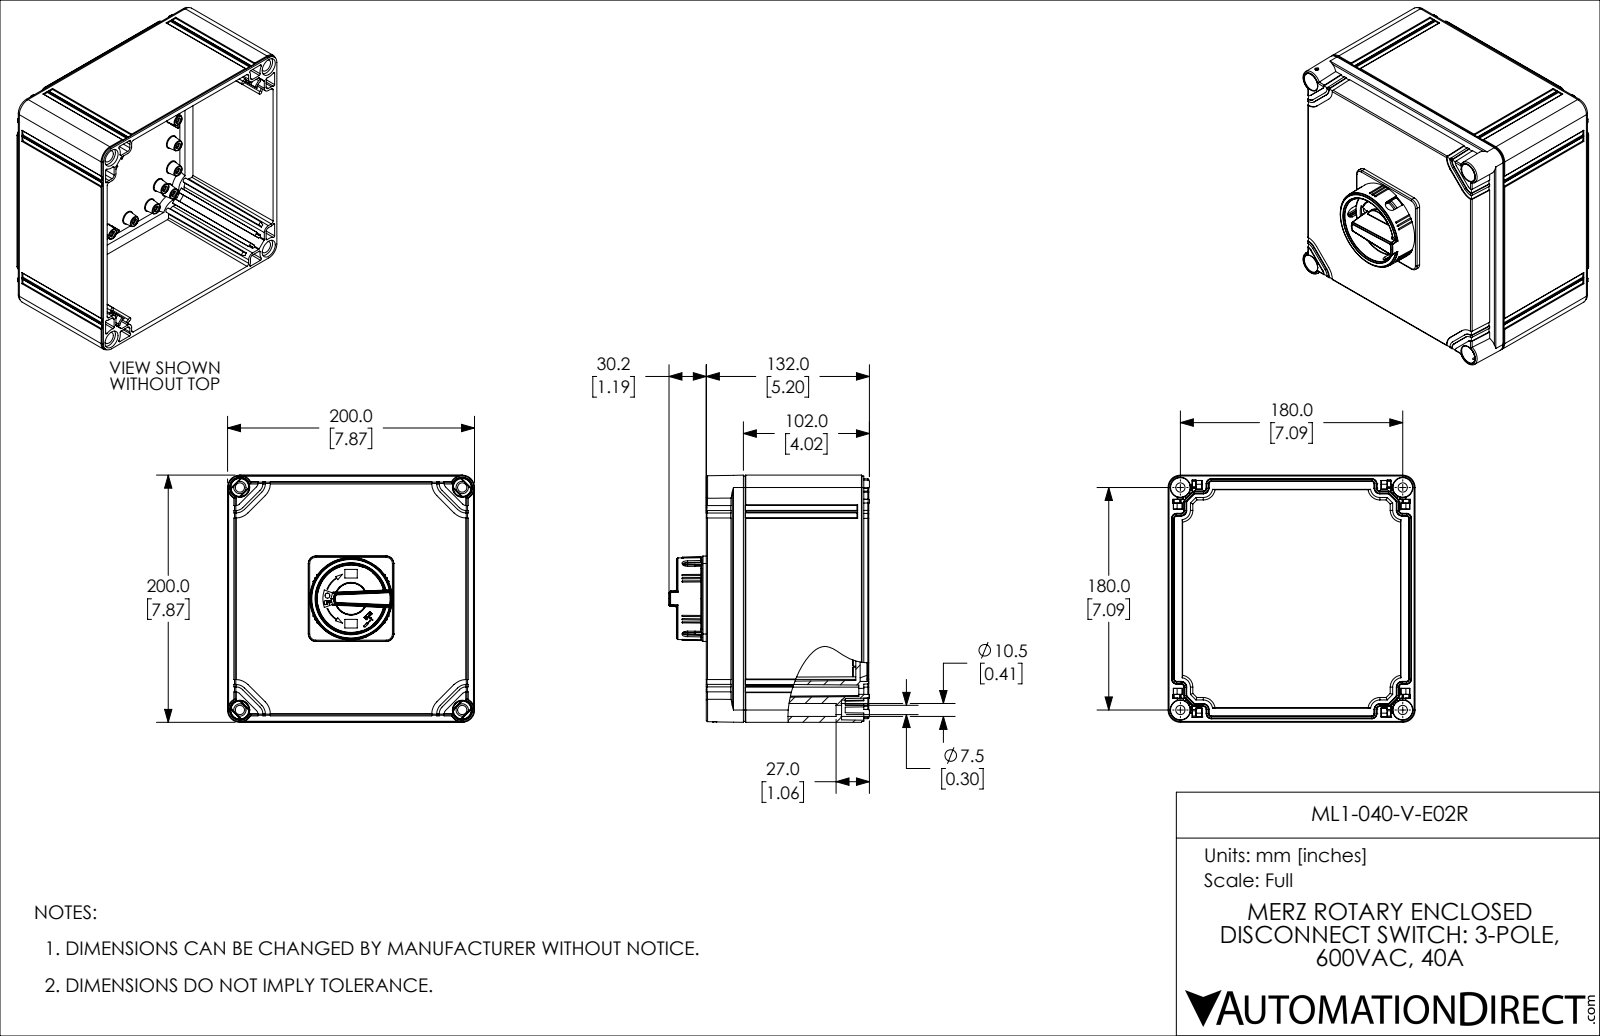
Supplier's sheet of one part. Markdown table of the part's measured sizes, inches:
| quantity | value |
| --- | --- |
| part name | ML1-040-V-E02R |
| STEP written by | SolidWorks 2019 (AUTOMOTIVE_DESIGN) |
| units | inches |
| bodies | 3 solids, 3426 faces (1296 planar, 641 cylindrical, 1489 other) |
| overall size | 7.874 × 7.874 × 6.386 |
| volume | 111.3 in³ |
| surface area | 733.3 in² |
| round holes (diameter × count) | 0.165 × 28, 0.197 × 28, 0.295 × 4, 0.394 × 4, 0.413 × 4, 0.087 × 2, 0.157 × 2, 0.669 × 1, 0.866 × 1 |
| round bosses / shafts (diameter × count) | 0.315 × 2, 0.945 × 1, 0.768 × 1, 0.591 × 1, 0.571 × 1, 0.551 × 1, 0.492 × 1, 0.236 × 1 |
| partial cylindrical surfaces (radius × count) | 0.02 × 174, 0.039 × 38, 0.008 × 22, 0.067 × 16, 0.01 × 15, 0.394 × 12, 0.157 × 8, 0.315 × 8 |
| main face-to-face distances | 1.28, 3.839, 0.138, 7.874, 5.118, 3.701, 4.98, 0.217, 0.02, 0.098 |
| hole center spacings | 0.984, 3.113, 3.549, 5.987, 2.953, 0.71, 0.812, 1.499 |
